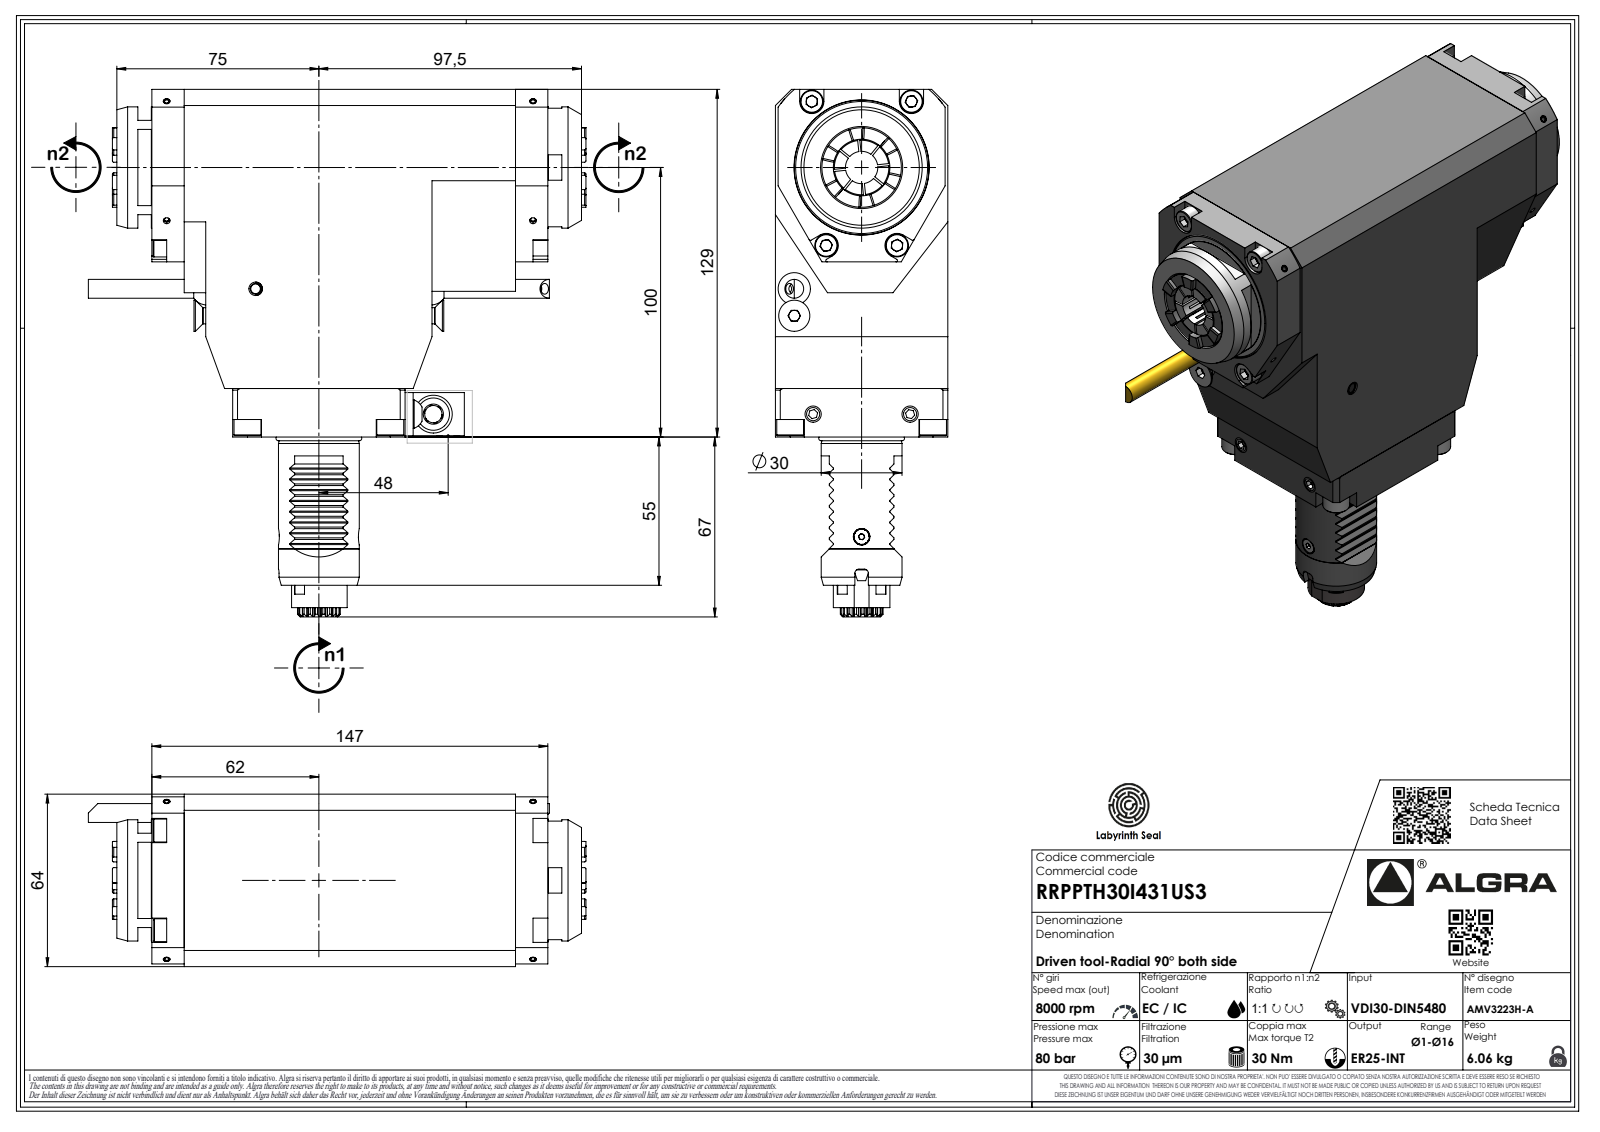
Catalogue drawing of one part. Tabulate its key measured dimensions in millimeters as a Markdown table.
| quantity | value |
| --- | --- |
| part name | RRPPTH30I431US3 |
| STEP written by | SolidWorks 2023 (AUTOMOTIVE_DESIGN) |
| units | millimeters |
| bodies | 2 solids, 1027 faces (673 planar, 185 cylindrical, 169 other) |
| overall size | 195.75 × 184.73 × 64 |
| volume | 984 607 mm³ |
| surface area | 80 752 mm² |
| round holes (diameter × count) | 4 × 2, 2.1 × 1 |
| round bosses / shafts (diameter × count) | 45 × 1, 30 × 1, 29.1 × 1, 21 × 1, 7 × 1, 6.37 × 1, 1.7 × 1 |
| partial cylindrical surfaces (radius × count) | 0.3 × 16, 35 × 8, 0.33 × 7, 0.52 × 7, 3.7 × 7, 0.5 × 4, 3 × 4, 4.5 × 4 |
| main face-to-face distances | 64, 129, 10, 43, 74, 117, 104, 20, 12, 18 |
| hole center spacings | 116.08 |
